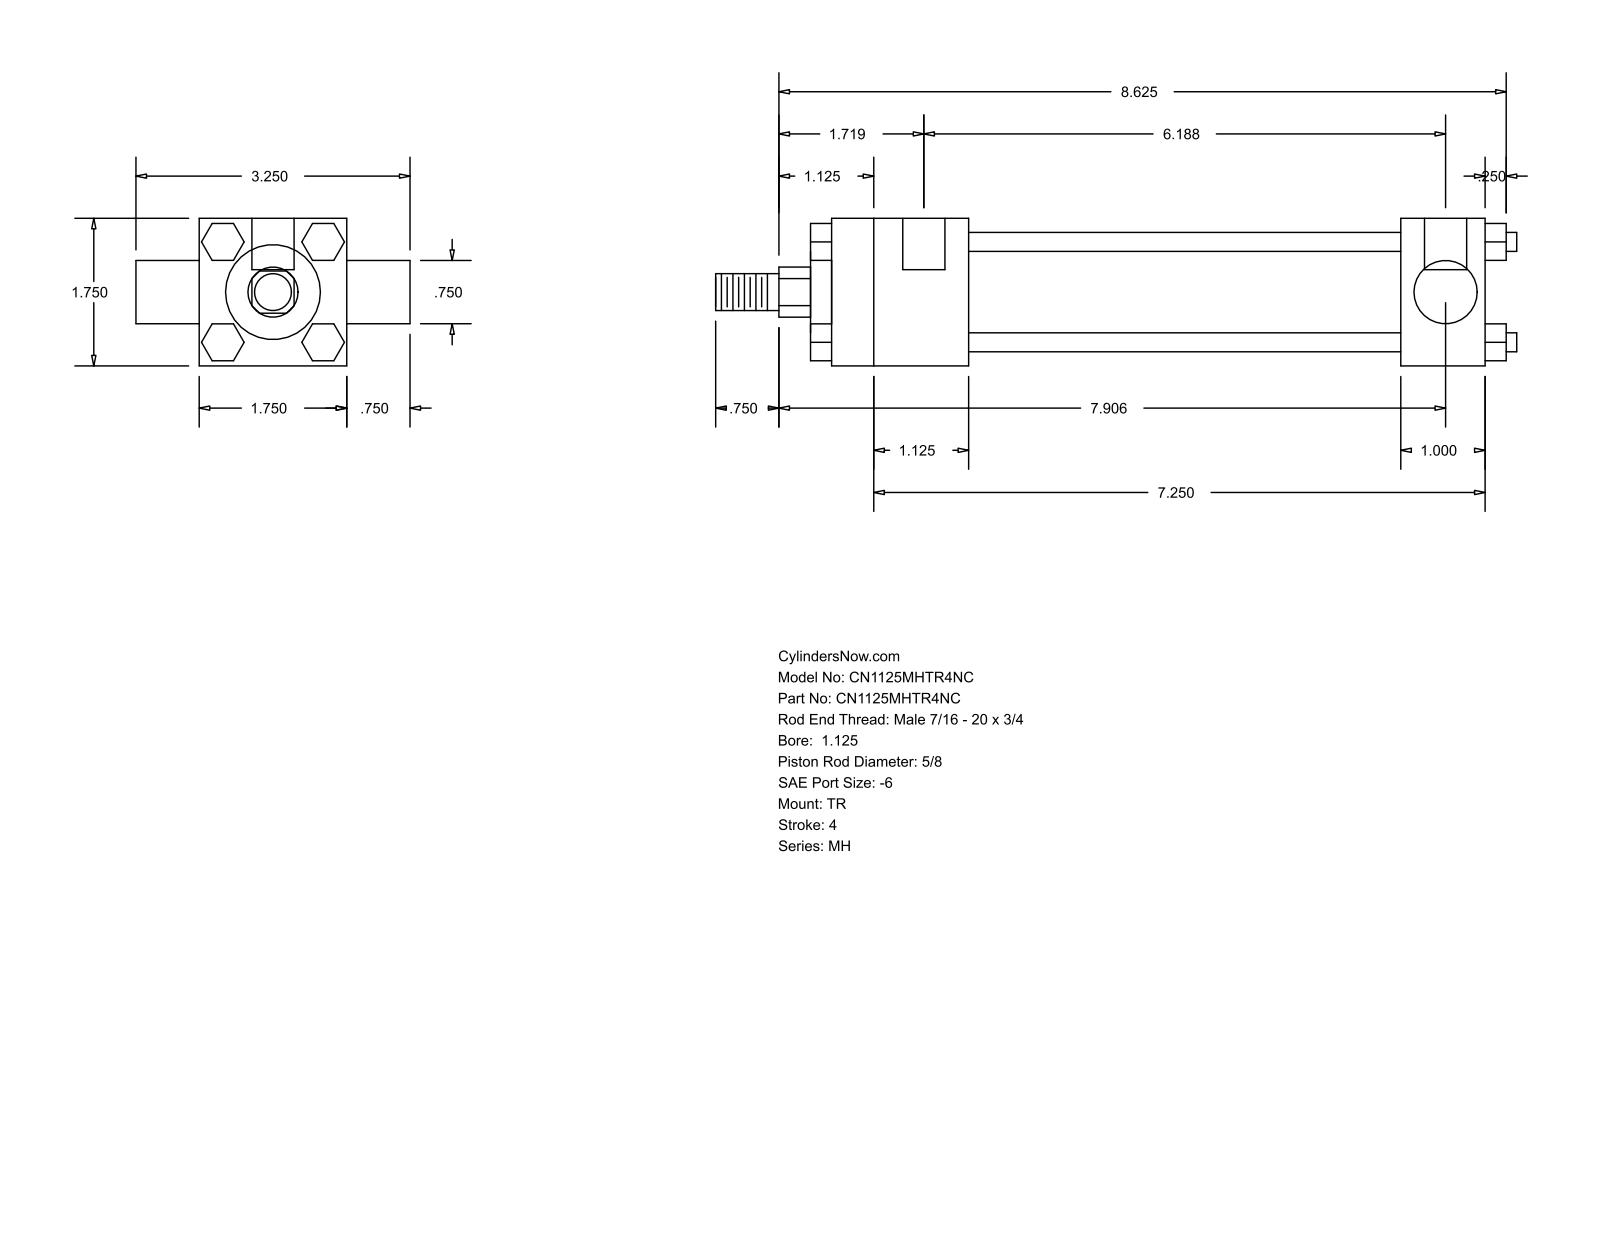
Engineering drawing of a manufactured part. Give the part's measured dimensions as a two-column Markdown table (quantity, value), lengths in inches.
| quantity | value |
| --- | --- |
| part name | MH_TR__0112_0.625 |
| STEP written by | GSSL Pune (CONFIG_CONTROL_DESIGN) |
| units | inches |
| bodies | 0 solids, 120 faces (92 planar, 28 cylindrical, 0 other) |
| overall size | 9.5 × 3.25 × 1.75 |
| round holes (diameter × count) | 0.219 × 3, 0.5 × 2 |
| round bosses / shafts (diameter × count) | 0.225 × 4, 1.375 × 1, 1.125 × 1, 0.75 × 1, 0.625 × 1, 0.437 × 1 |
| partial cylindrical surfaces (radius × count) | 0.297 × 1 |
| main face-to-face distances | 1.75, 0.25, 8, 0.437, 1, 5.125, 6.125, 1.625, 6.75, 7.75 |
| hole center spacings | 0.125, 6.063, 6.187 |
